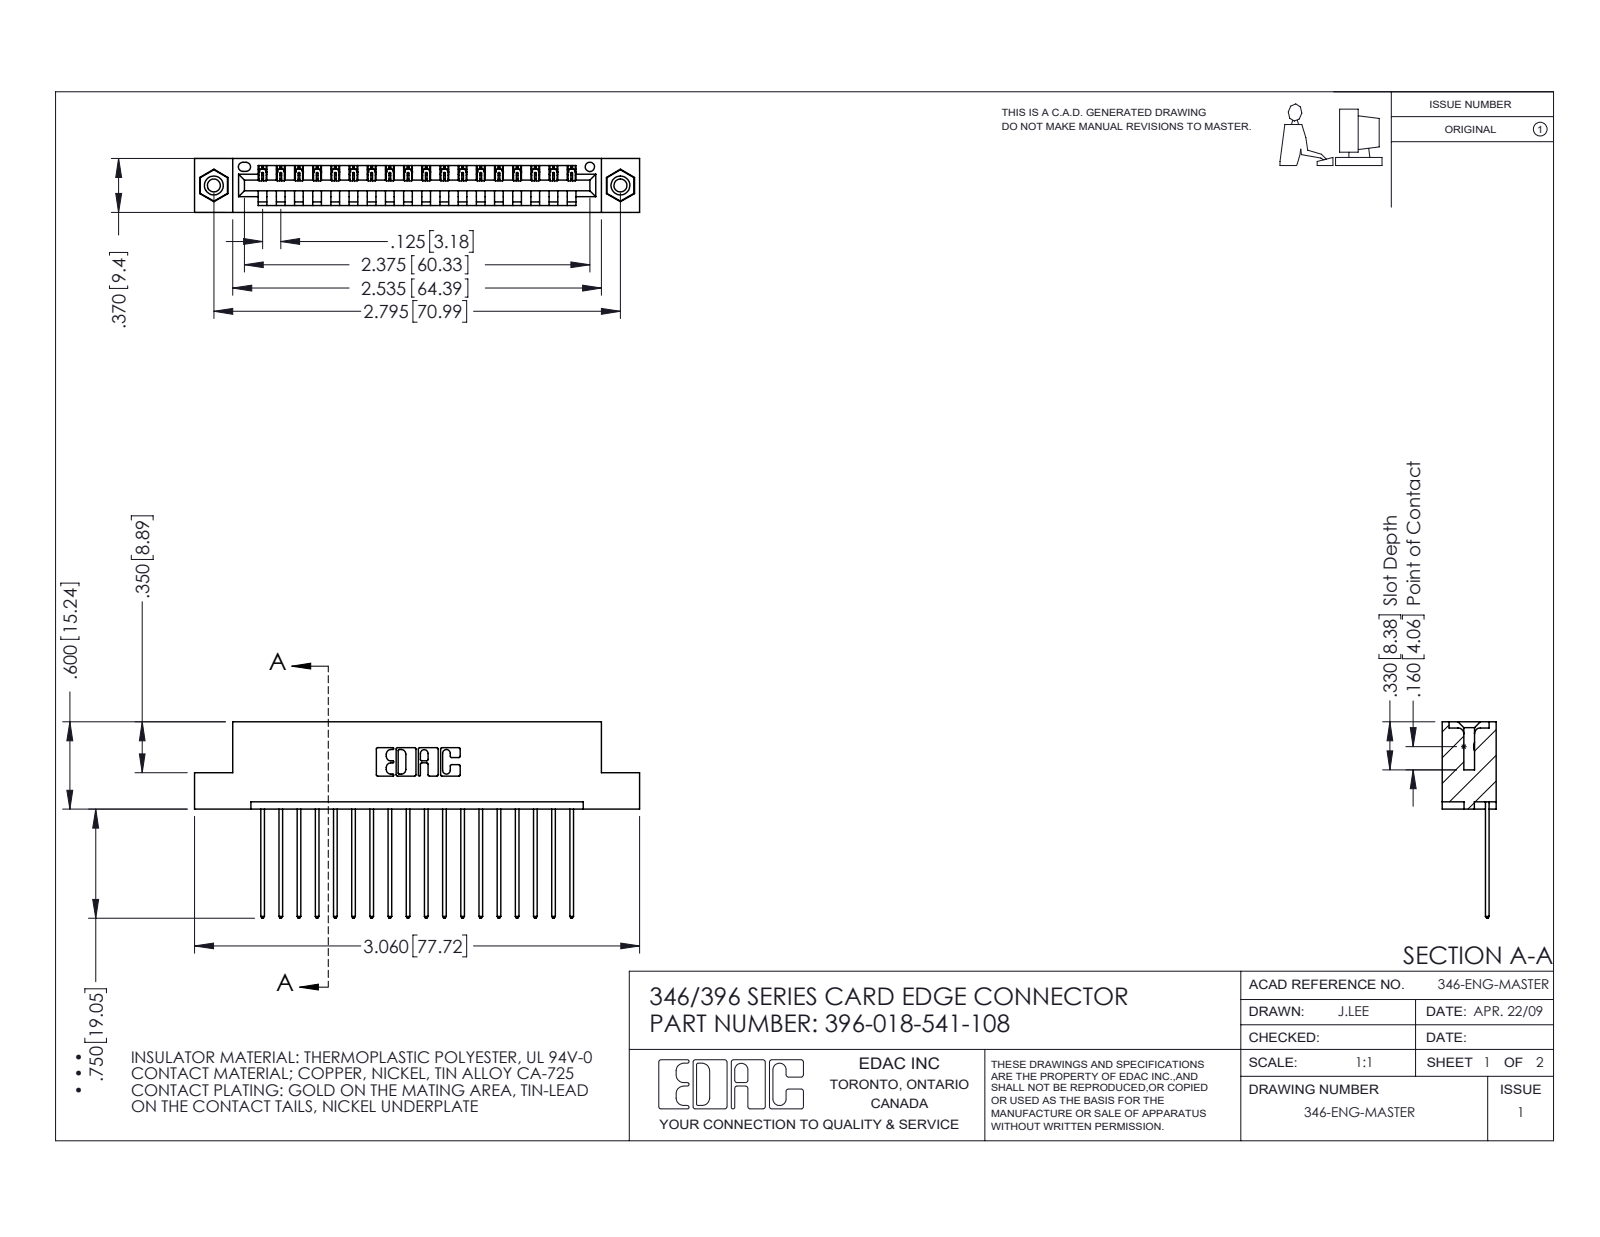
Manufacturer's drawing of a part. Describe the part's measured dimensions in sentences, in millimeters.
The part is named "345-250-001_345-250-003-102; 345-292-001_345-293-141; 346 Part_Flush Mounting Lugs - 0.156 Dia-TI; 396-018-541-108". Its 3-D file was written by "SolidWorks 2016 (CONFIG_CONTROL_DESIGN)". It is 21 solids with 1226 faces: 828 planar, 382 cylindrical and 16 other. Overall it measures 77.7 by 34.3 by 9.4 millimeters. Its volume is 7 330 cubic millimeters and its surface area 9 277 square millimeters. Round holes: 2 of diameter 2.3, 2 of diameter 3.2, 2 of diameter 4, 1 of diameter 1.6. Round bosses or shafts: 2 of diameter 3.9. Partial cylindrical surfaces (rounded edges, fillets, slot ends): 36 of radius 0.2, 36 of radius 0.3, 22 of radius 0.3, 6 of radius 0.2, 6 of radius 0.8, 3 of radius 0.7, 2 of radius 0.8, 2 of radius 1. The main face-to-face distances are 1.2, 8.2, 6.4, 9.4, 1.8, 7.6, 0.6, 3.8, 5.6, 2.5. The hole center spacings are 6.2, 65.7, 71.
